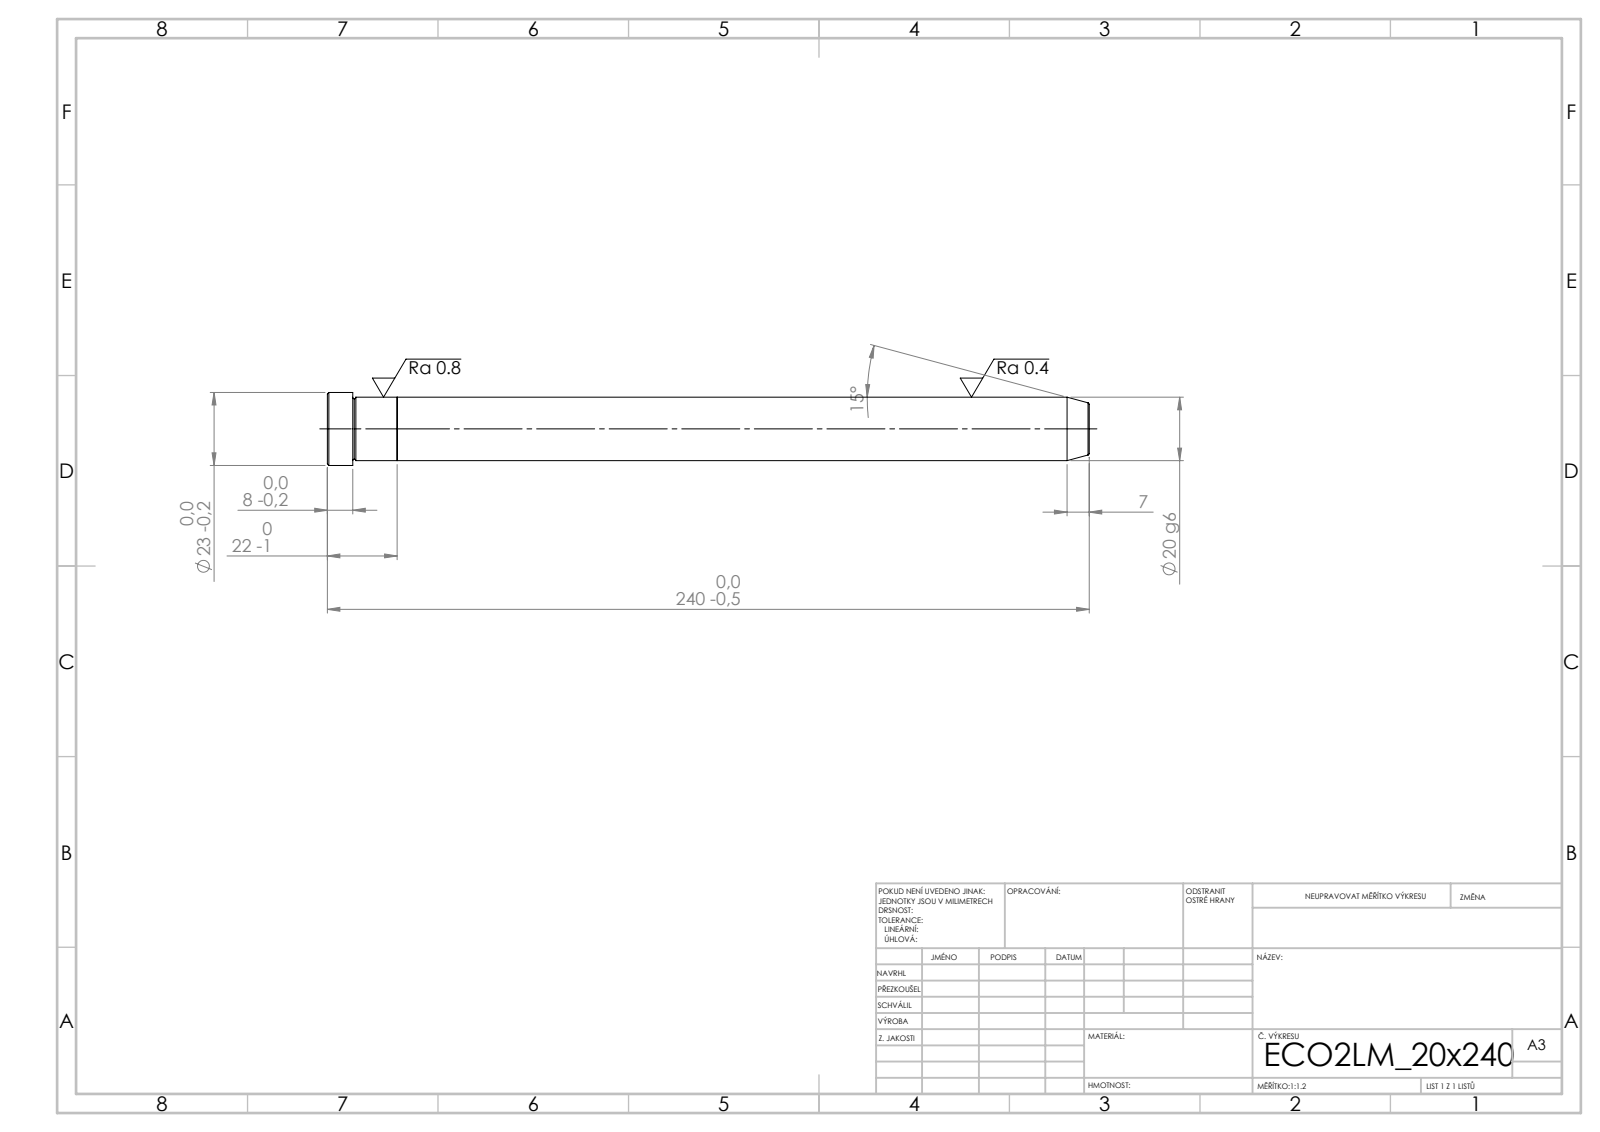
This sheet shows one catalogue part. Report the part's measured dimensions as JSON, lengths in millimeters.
{"step_written_by": "SolidWorks 2019 (CONFIG_CONTROL_DESIGN)", "units": "millimeters", "bodies": {"solids": 2, "faces": 21, "planar": 5, "cylindrical": 6, "other": 10}, "overall_size": [240, 23, 23], "volume_mm3": 75788, "surface_area_mm2": 16486, "round_bosses_or_shafts": [[23, 1], [20, 1]], "face_to_face_distances": [22, 218, 240, 232, 14, 8]}
